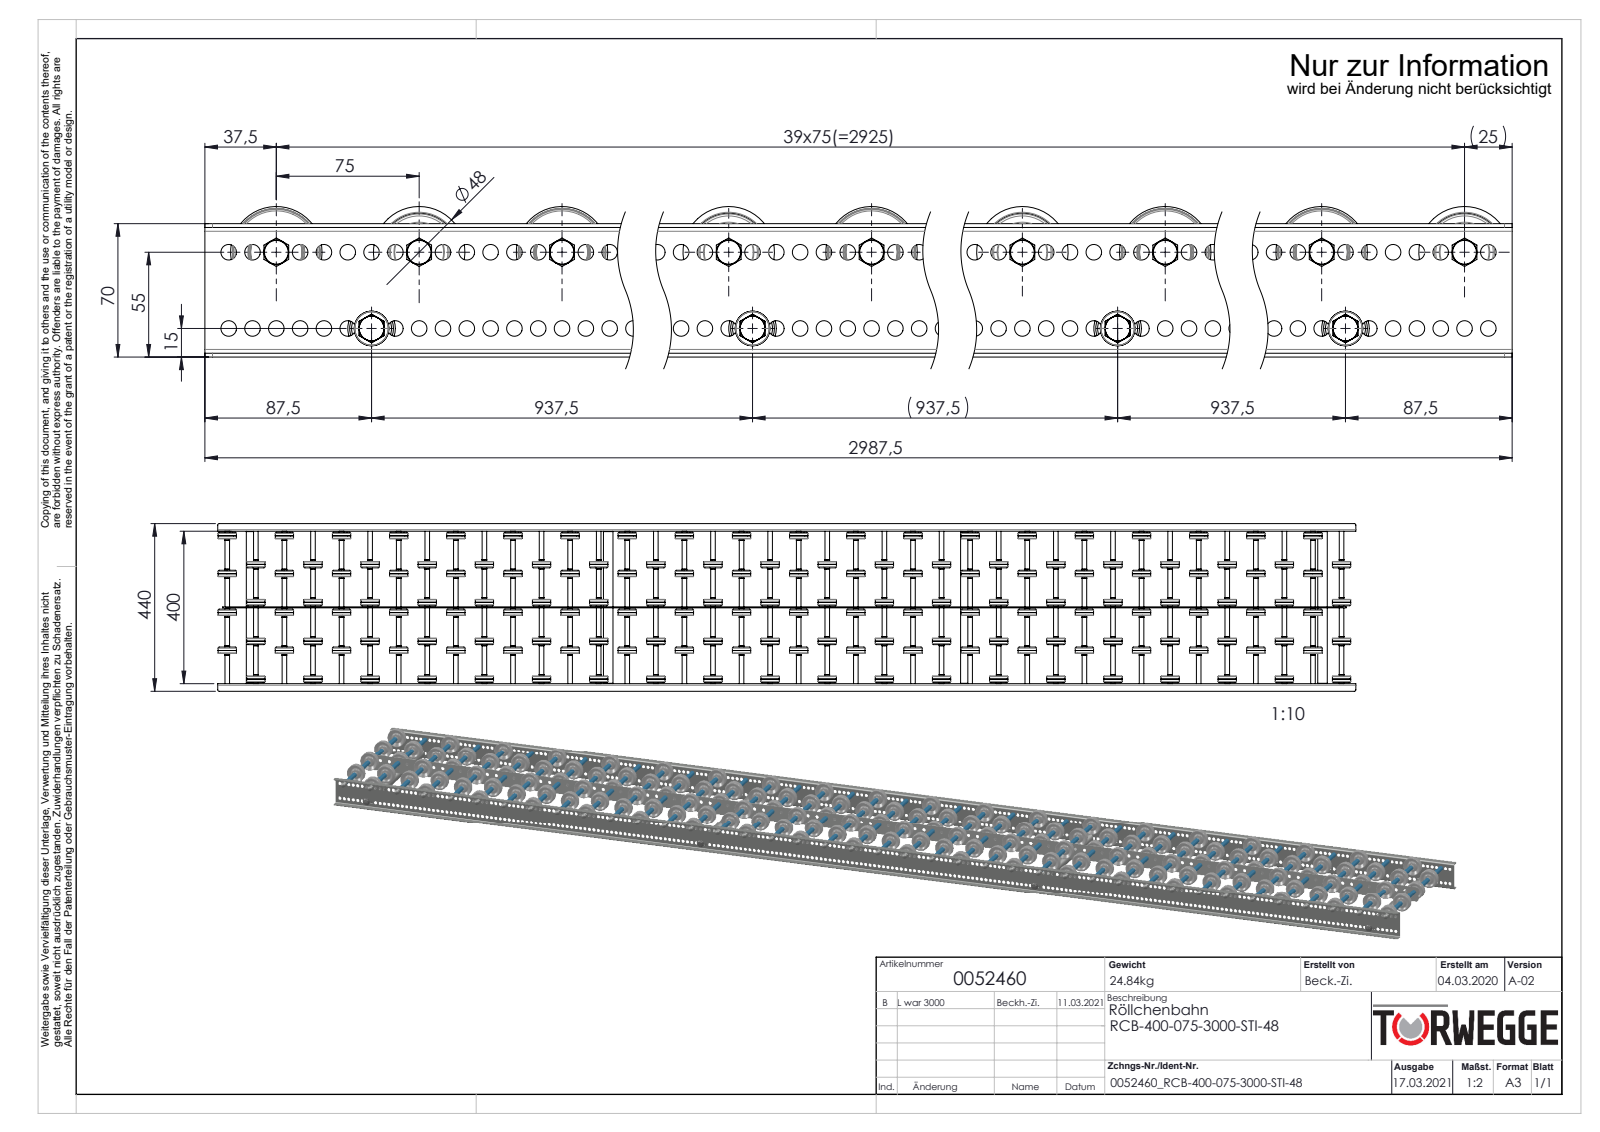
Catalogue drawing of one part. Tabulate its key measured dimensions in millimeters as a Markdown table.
| quantity | value |
| --- | --- |
| part name | Profil_LRB-20x70x20x2_KFG_S109080_U-PROFIL-20-70-20-2-LRB-L=2987,5; S100994_Sperrzahnschraube_M08x16-8.8-A2K; Röllchenachse-für-Konfiguration_EL400 Stahl; Hutmutter_DIN_1587_M8 (+6 more) |
| STEP written by | SolidWorks 2020 (AUTOMOTIVE_DESIGN) |
| units | millimeters |
| bodies | 623 solids, 18978 faces (3810 planar, 7440 cylindrical, 7728 other) |
| overall size | 2987.5 × 440 × 79 |
| volume | 6 485 000 mm³ |
| surface area | 5 019 000 mm² |
| round holes (diameter × count) | 8.2 × 476, 8.5 × 118, 6.65 × 40, 8 × 40, 9.65 × 40, 15 × 40, 41 × 40, 6.8 × 4, 21 × 4 |
| round bosses / shafts (diameter × count) | 48 × 40, 13 × 40, 12.5 × 40, 12.4 × 40, 12 × 40, 11.5 × 40, 25 × 4, 8 × 4 |
| partial cylindrical surfaces (radius × count) | 4 × 8, 2 × 4, 5 × 4 |
| main face-to-face distances | 2, 201.5, 402, 99.5, 75, 201, 12, 186.5, 87, 111.5 |
| hole center spacings | 12.5, 25, 37.5, 50, 62.5, 75, 87.5, 100 |
